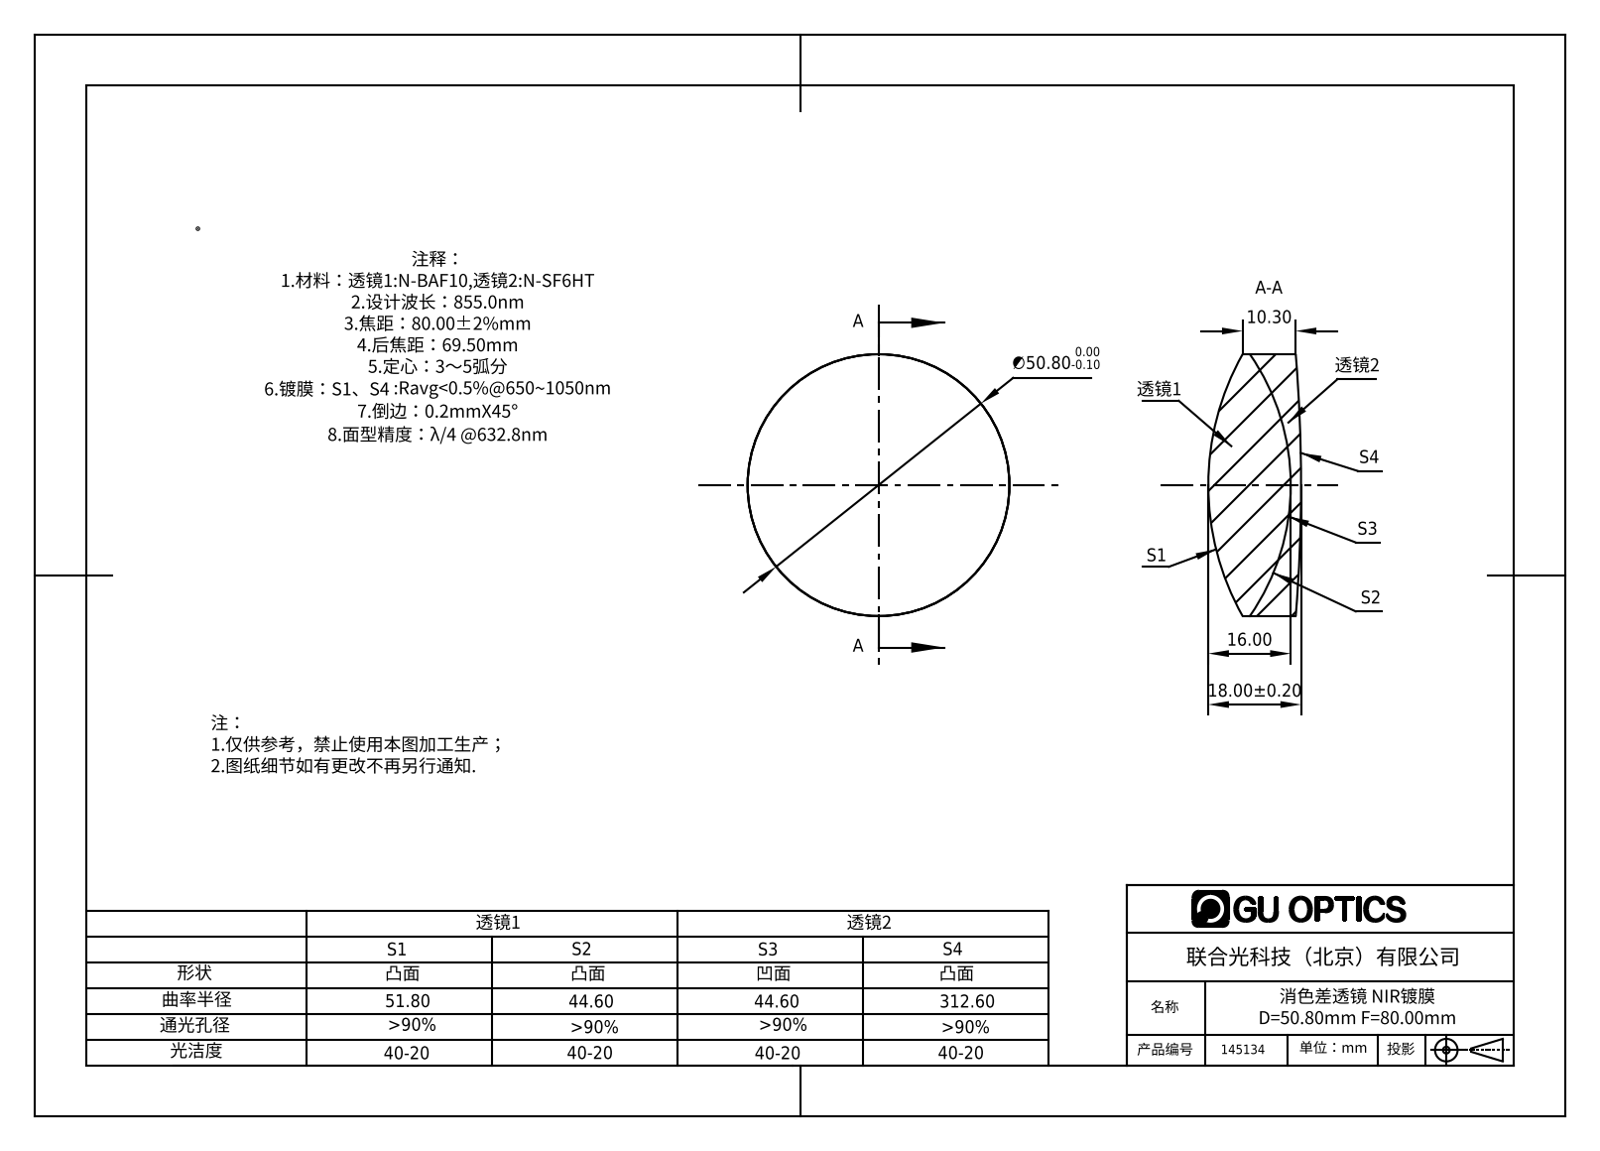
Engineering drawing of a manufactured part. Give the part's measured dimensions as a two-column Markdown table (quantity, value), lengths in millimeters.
| quantity | value |
| --- | --- |
| part name | 145134 |
| STEP written by | SolidWorks 2016 (AUTOMOTIVE_DESIGN) |
| units | millimeters |
| bodies | 2 solids, 12 faces (0 planar, 4 cylindrical, 8 other) |
| overall size | 50.8 × 50.8 × 18 |
| volume | 28 846 mm³ |
| surface area | 10 291 mm² |
| round bosses / shafts (diameter × count) | 50.8 × 1 |
